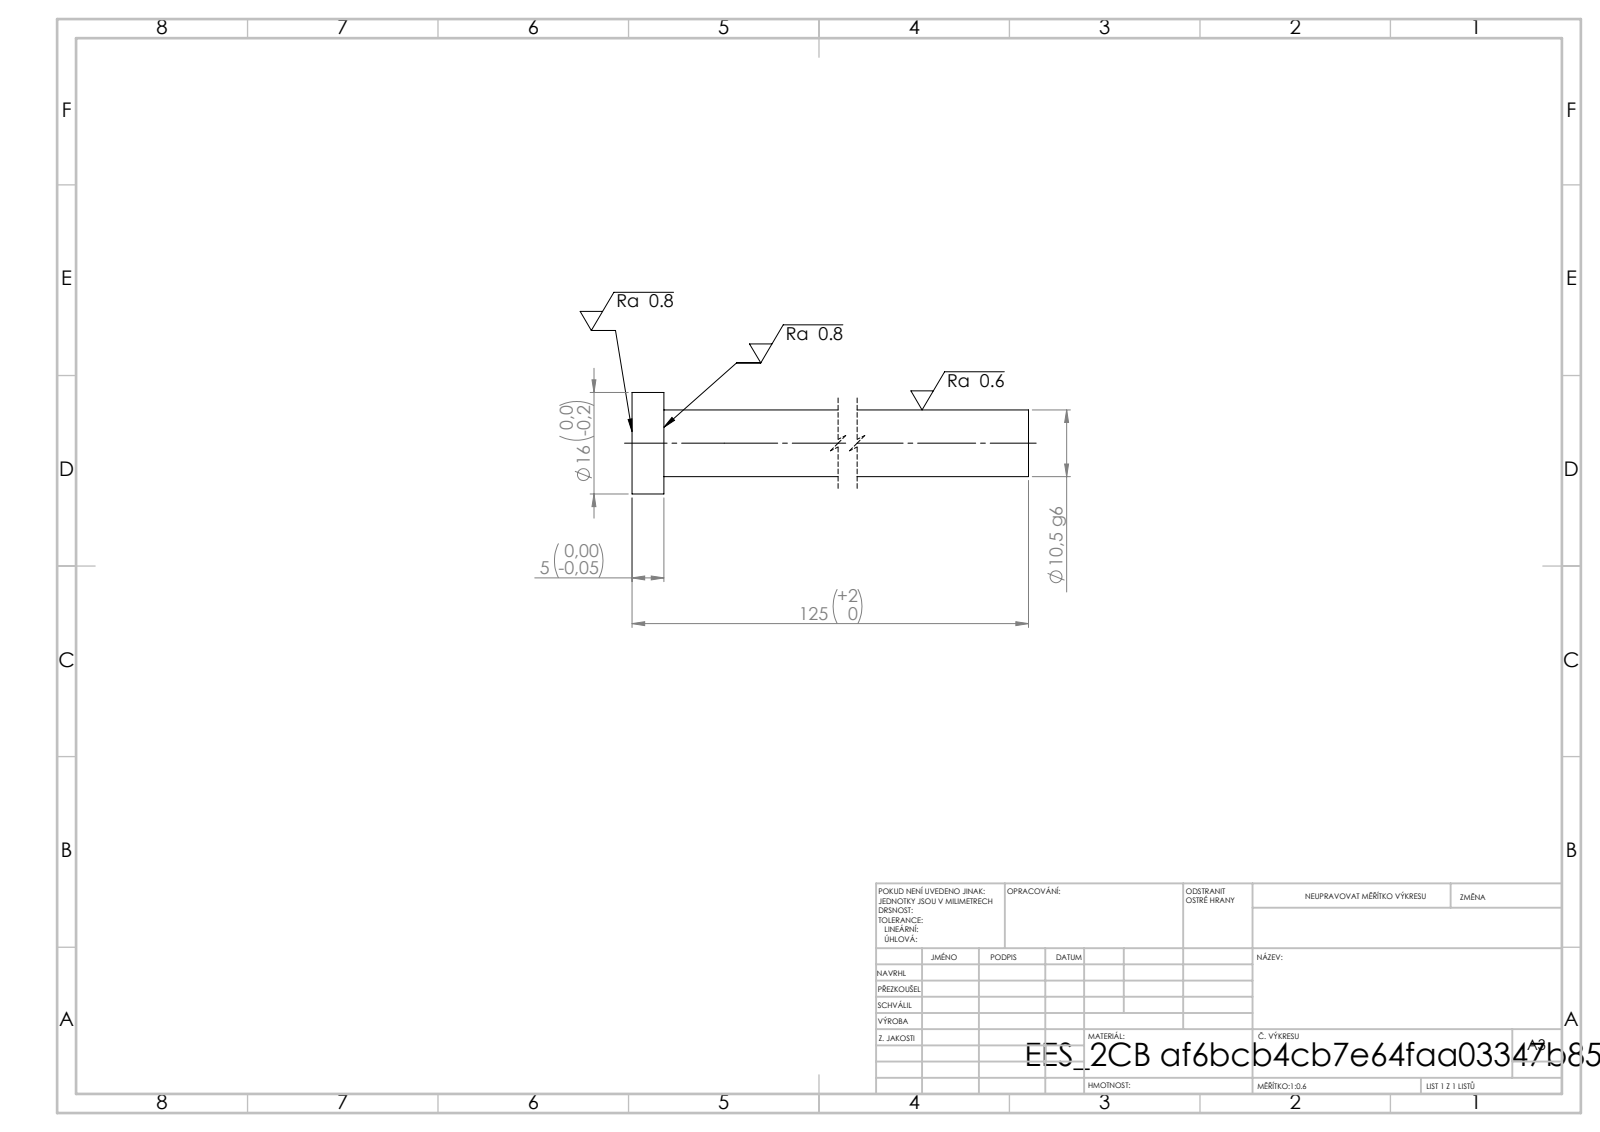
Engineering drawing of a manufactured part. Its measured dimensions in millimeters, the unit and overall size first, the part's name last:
Units: millimetres
Overall size (bounding box): 125 × 16 × 16
Round bosses / shafts (diameter × count): ⌀16 ×1, ⌀10.5 ×1
Main face-to-face distances: 5, 125, 120
Volume: 11 396 mm³ · Surface area: 4 612 mm²
Bodies: 1 solid, 7 faces (3 planar, 4 cylindrical, 0 other)
STEP written by: SolidWorks 2019 (CONFIG_CONTROL_DESIGN)
